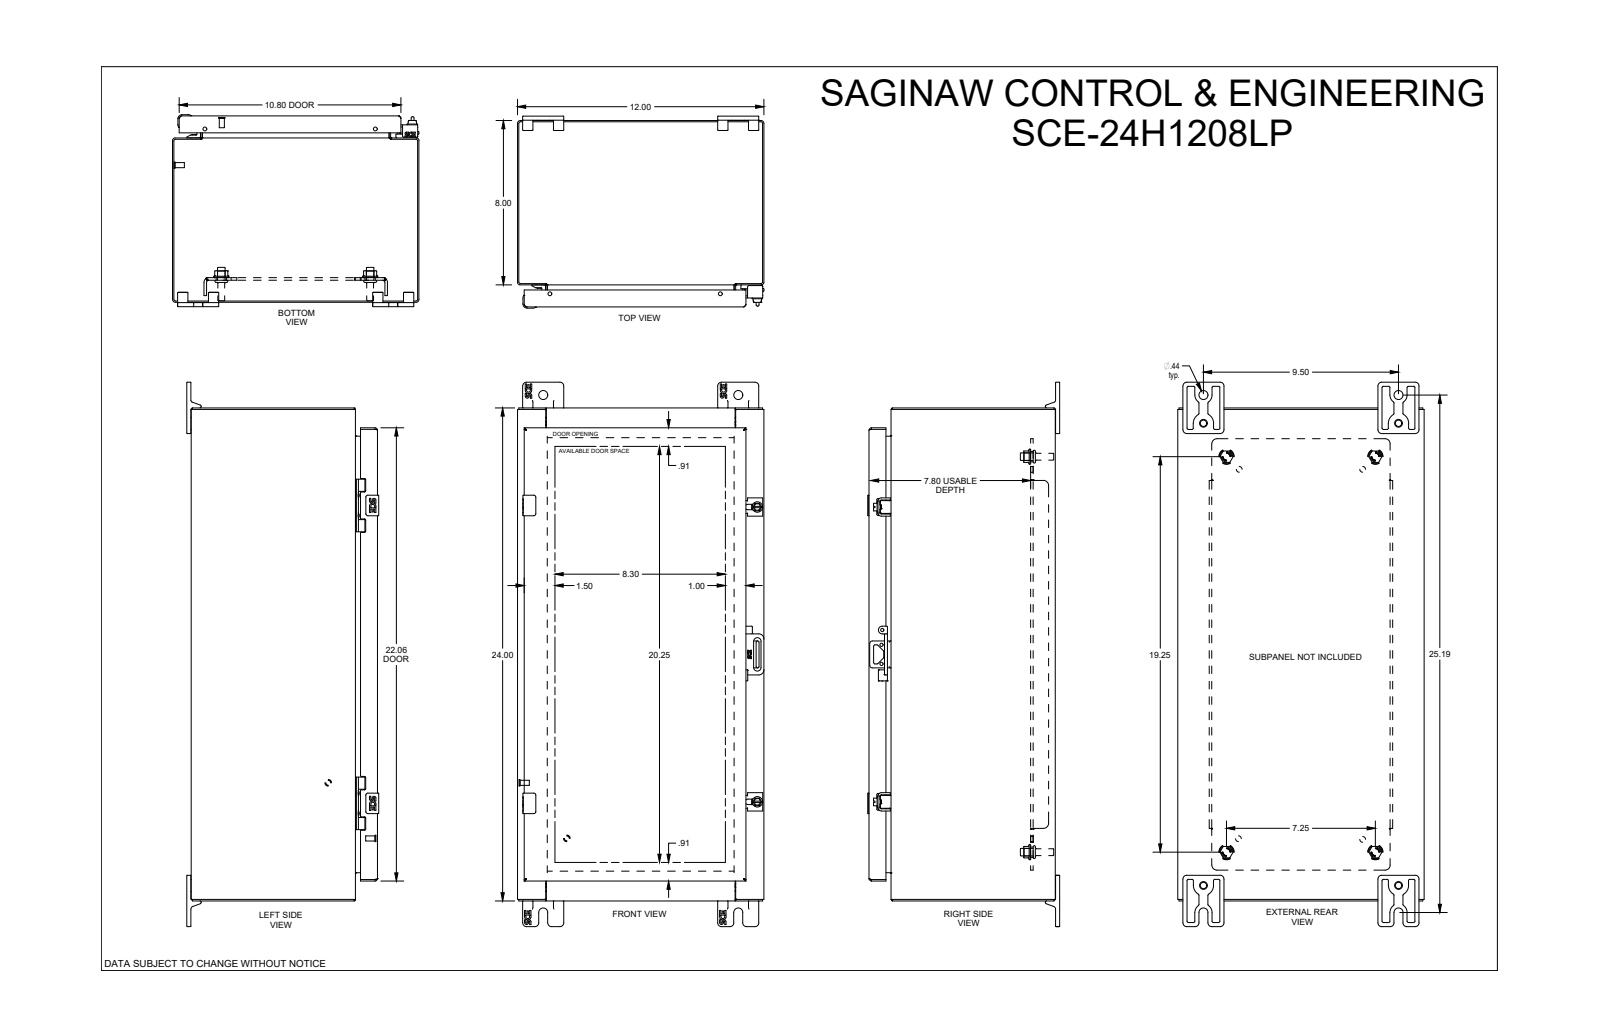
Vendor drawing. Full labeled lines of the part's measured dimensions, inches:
Part name (STEP PRODUCT): SCE-24H1208LP
STEP written by: SolidWorks 2019 (CONFIG_CONTROL_DESIGN)
Units: inches
Bodies: 0 solids, 3917 faces (1504 planar, 1128 cylindrical, 1285 other)
Overall size (bounding box): 26.5 × 12 × 9.348
Round holes (diameter × count): ⌀0.172 ×4, ⌀0.205 ×4, ⌀0.218 ×4, ⌀0.244 ×4, ⌀0.266 ×4, ⌀0.281 ×4, ⌀0.31 ×4, ⌀0.312 ×4, ⌀0.367 ×4, ⌀0.375 ×4, ⌀0.437 ×4, ⌀0.5 ×4
Round bosses / shafts (diameter × count): ⌀0.17 ×7, ⌀0.25 ×6, ⌀0.248 ×5, ⌀0.59 ×4, ⌀0.376 ×4, ⌀0.366 ×4, ⌀0.332 ×4, ⌀0.24 ×4
Partial cylindrical surfaces — rounded edges, fillets, slot ends (radius × count): R0.025 ×125, R0.01 ×114, R0.015 ×56, R0.03 ×37, R0.062 ×35, R0.06 ×30, R0.063 ×28, R0.185 ×21
Main face-to-face distances: 0.075, 11.925, 0.075, 8.998, 8.923, 9.073, 8.998, 23.925, 11.85, 12
Hole centre spacings: 14.5, 0.02, 0.493, 0.875, 0.985, 1.977, 8.531, 20.905
